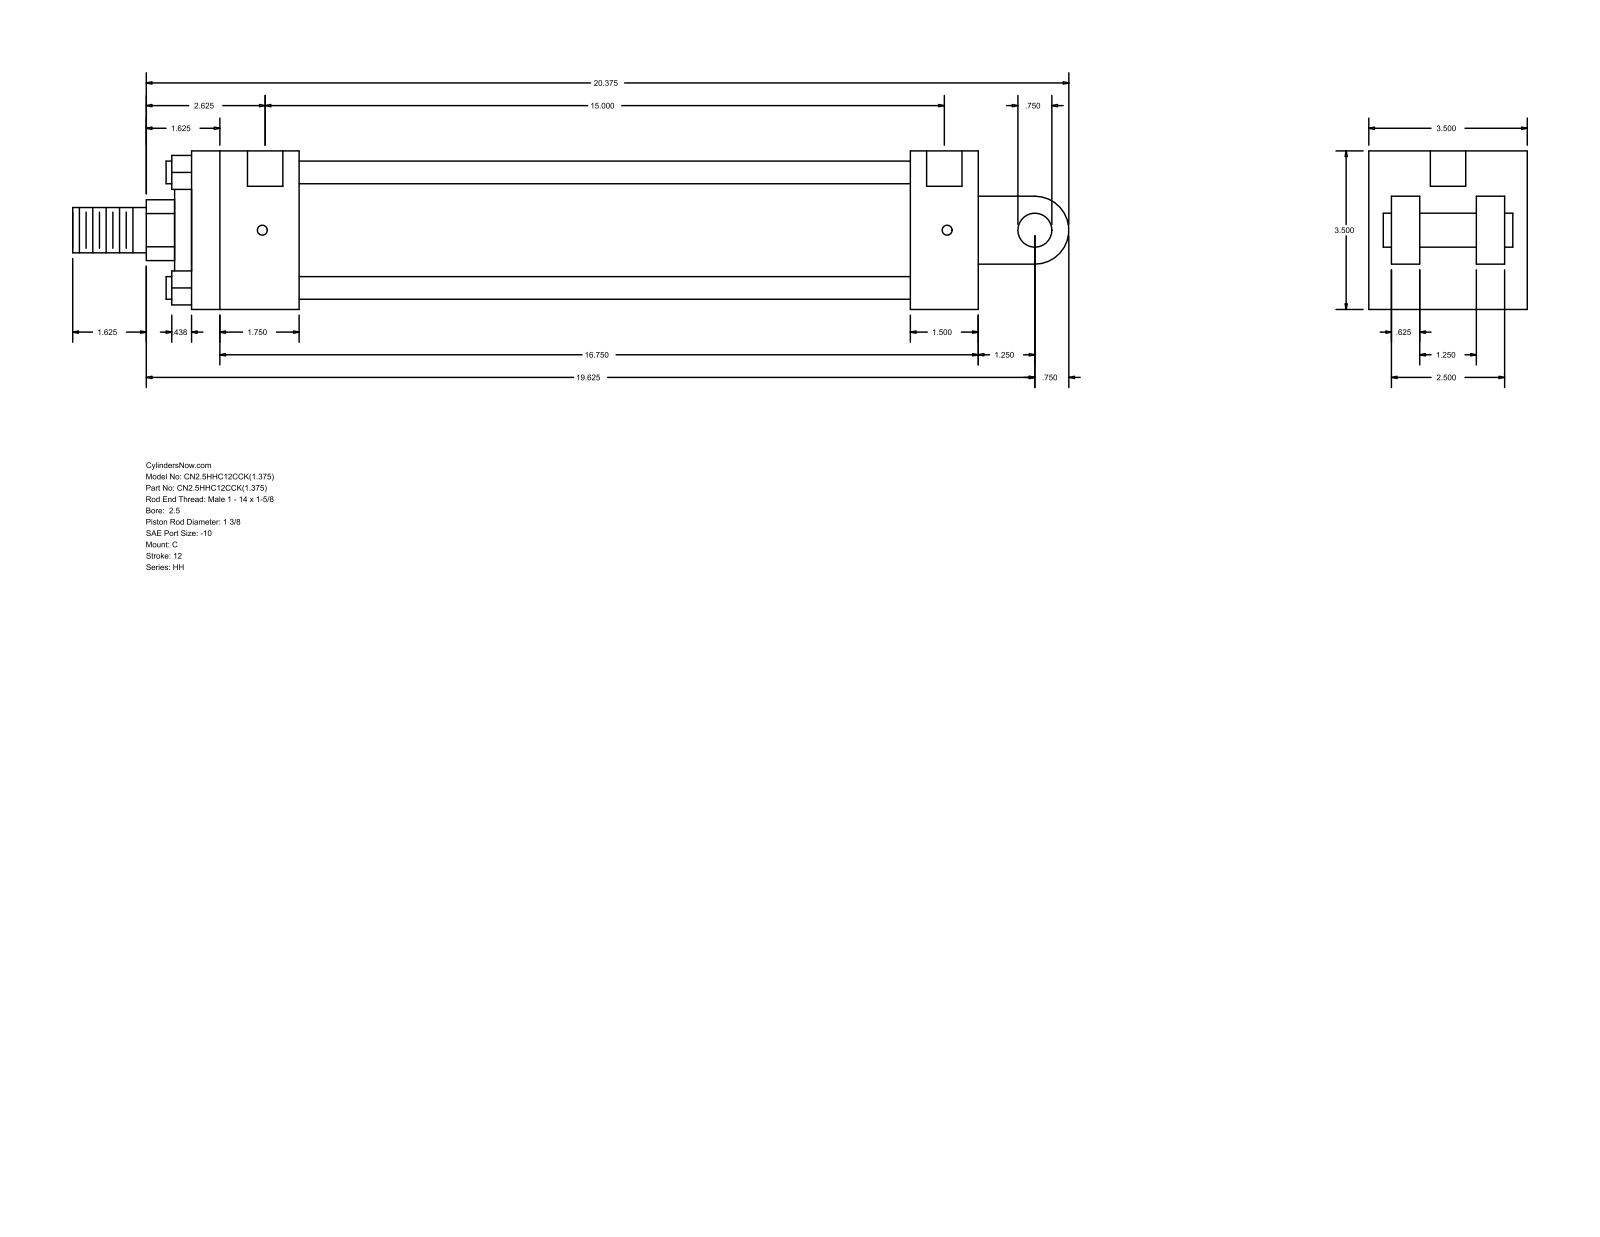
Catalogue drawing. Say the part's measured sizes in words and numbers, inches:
The part is named "HH_C__0250_1.375". Its 3-D file was written by "GSSL Pune (CONFIG_CONTROL_DESIGN)". It is 0 solids with 99 faces: 70 planar, 29 cylindrical and 0 other. Overall it measures 22 by 3.5 by 3.5 inches. Round holes: 4 of diameter 0.219, 2 of diameter 0.781. Round bosses or shafts: 4 of diameter 0.5, 1 of diameter 2.875, 1 of diameter 2, 1 of diameter 1.375, 1 of diameter 1, 1 of diameter 0.75. Partial cylindrical surfaces (rounded edges, fillets, slot ends): 1 of radius 0.672, 1 of radius 0.75. The main face-to-face distances are 3.5, 17.375, 2.5, 0.5, 15.875, 1.5, 2.375, 13.5, 15, 3. The hole center spacings are 0.062, 15.063, 15.125, 15.
